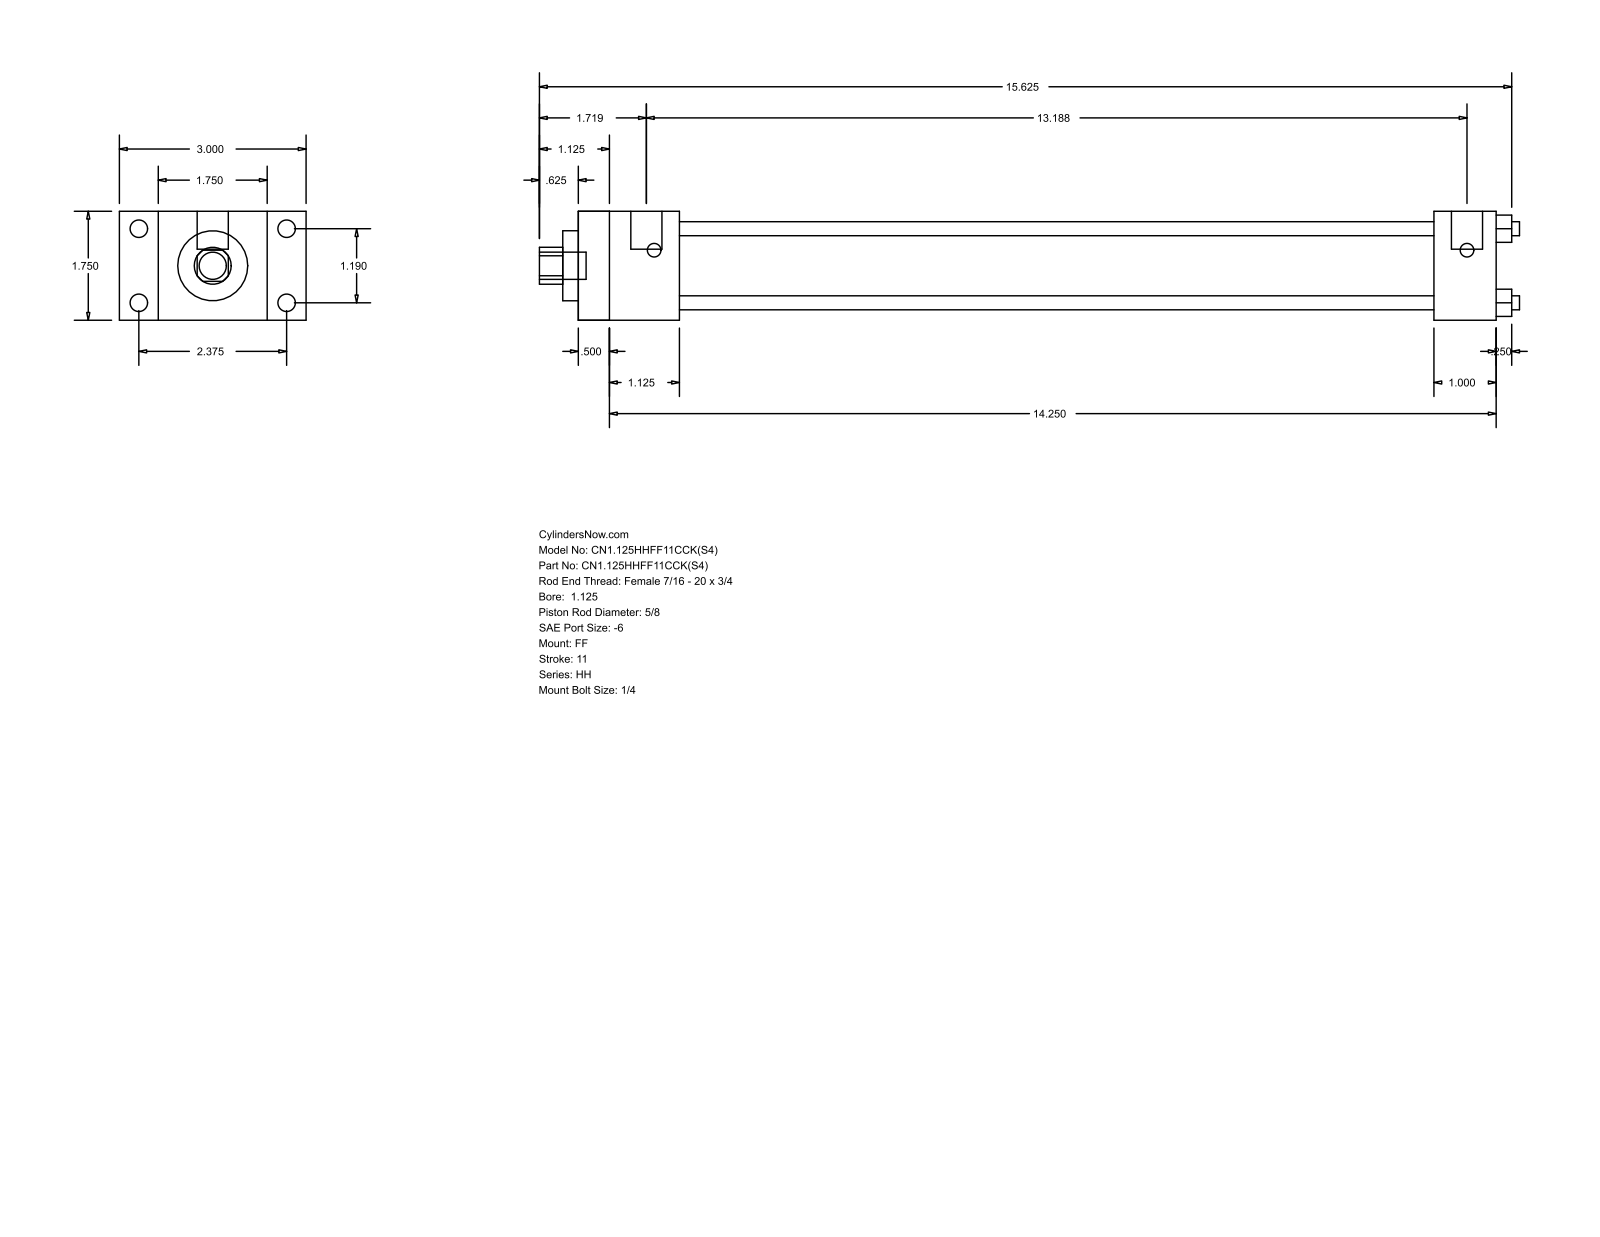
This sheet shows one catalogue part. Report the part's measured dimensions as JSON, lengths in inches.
{"part_name": "HH_FF__0112_0.625", "step_written_by": "GSSL Pune (CONFIG_CONTROL_DESIGN)", "units": "inches", "bodies": {"solids": 0, "faces": 92, "planar": 64, "cylindrical": 28, "other": 0}, "overall_size": [15.75, 3, 1.75], "round_holes": [[0.225, 4], [0.625, 1], [1.125, 1], [1.375, 1]], "round_bosses_or_shafts": [[0.281, 4], [0.219, 4], [0.5, 2], [0.437, 1]], "partial_cylinders_radius": [[0.297, 1]], "face_to_face_distances": [1.75, 14.75, 0.5, 14.25, 0.625, 2.375, 1.125, 1.625, 13.75, 13.25], "hole_center_spacings": [0.841, 1.19, 1.683]}
